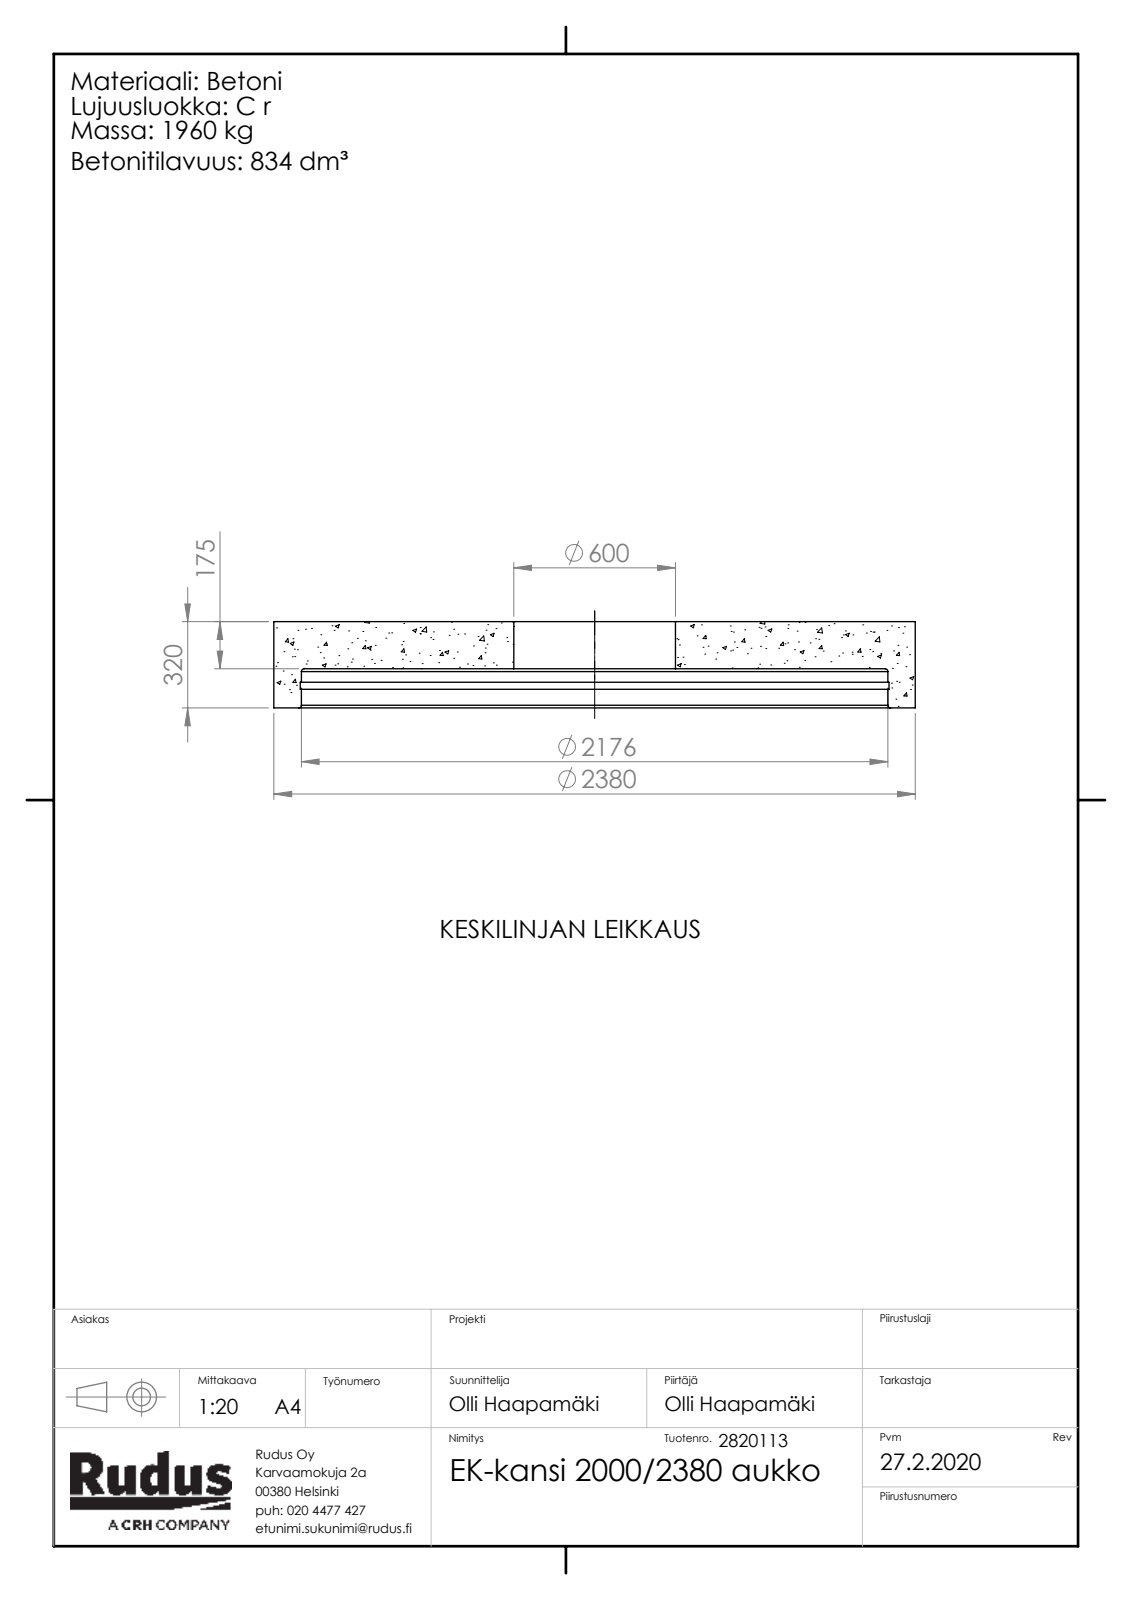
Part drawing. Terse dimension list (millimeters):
name: EK-osa-kansi_Aukko; Rudus 2820113 EK-kansi 2000_2380 aukko
written by: SolidWorks 2019 (CONFIG_CONTROL_DESIGN)
unit: mm
bodies: 1 solid, 96 faces (13 planar, 17 cylindrical, 66 other)
size: 2380 × 2380 × 320
volume: 834 100 000 mm³; area: 12 050 000 mm²
holes: 1× ⌀600, 1× ⌀2176, 1× ⌀2184
bosses: 1× ⌀2380
rounds: 1× R1187
face distances: 175, 145, 320, 69, 76, 251, 95, 26, 50, 225
